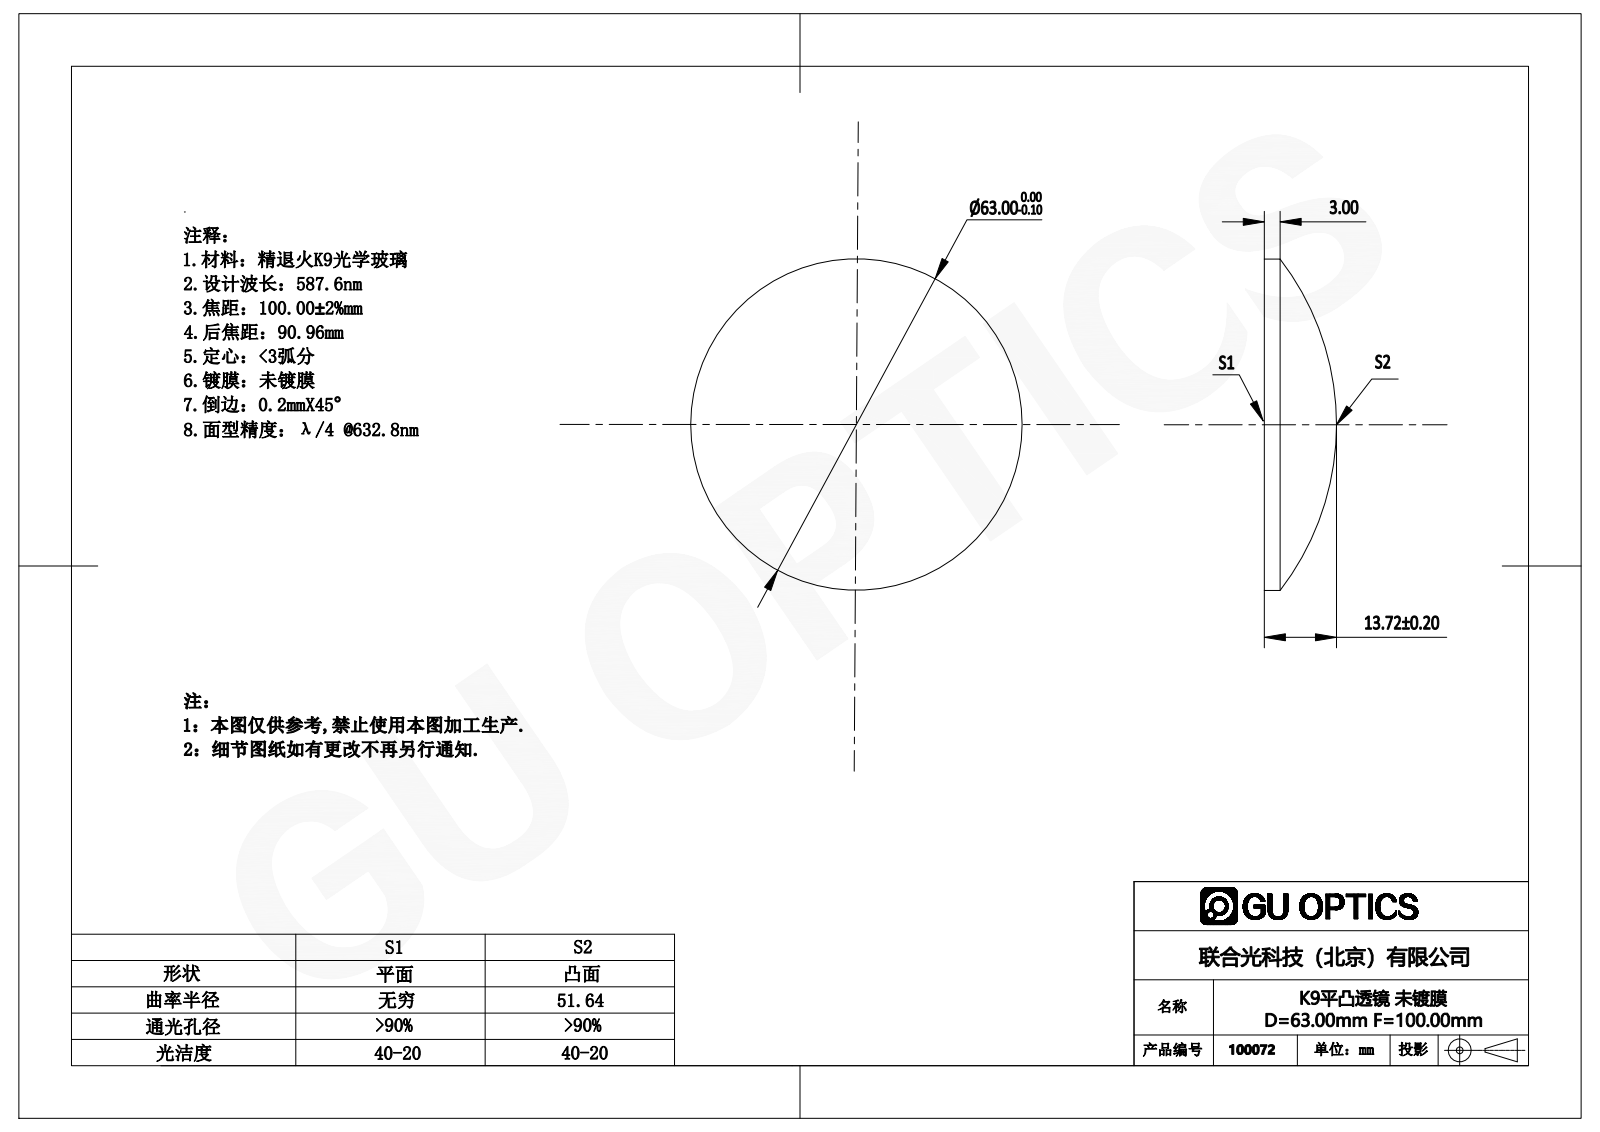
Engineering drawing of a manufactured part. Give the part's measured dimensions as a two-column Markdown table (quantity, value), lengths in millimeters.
| quantity | value |
| --- | --- |
| part name | 100072 |
| STEP written by | SolidWorks 2016 (AUTOMOTIVE_DESIGN) |
| units | millimeters |
| bodies | 1 solid, 5 faces (1 planar, 2 cylindrical, 2 other) |
| overall size | 63 × 63 × 13.72 |
| volume | 26 705 mm³ |
| surface area | 7 189 mm² |
| round bosses / shafts (diameter × count) | 63 × 1 |
